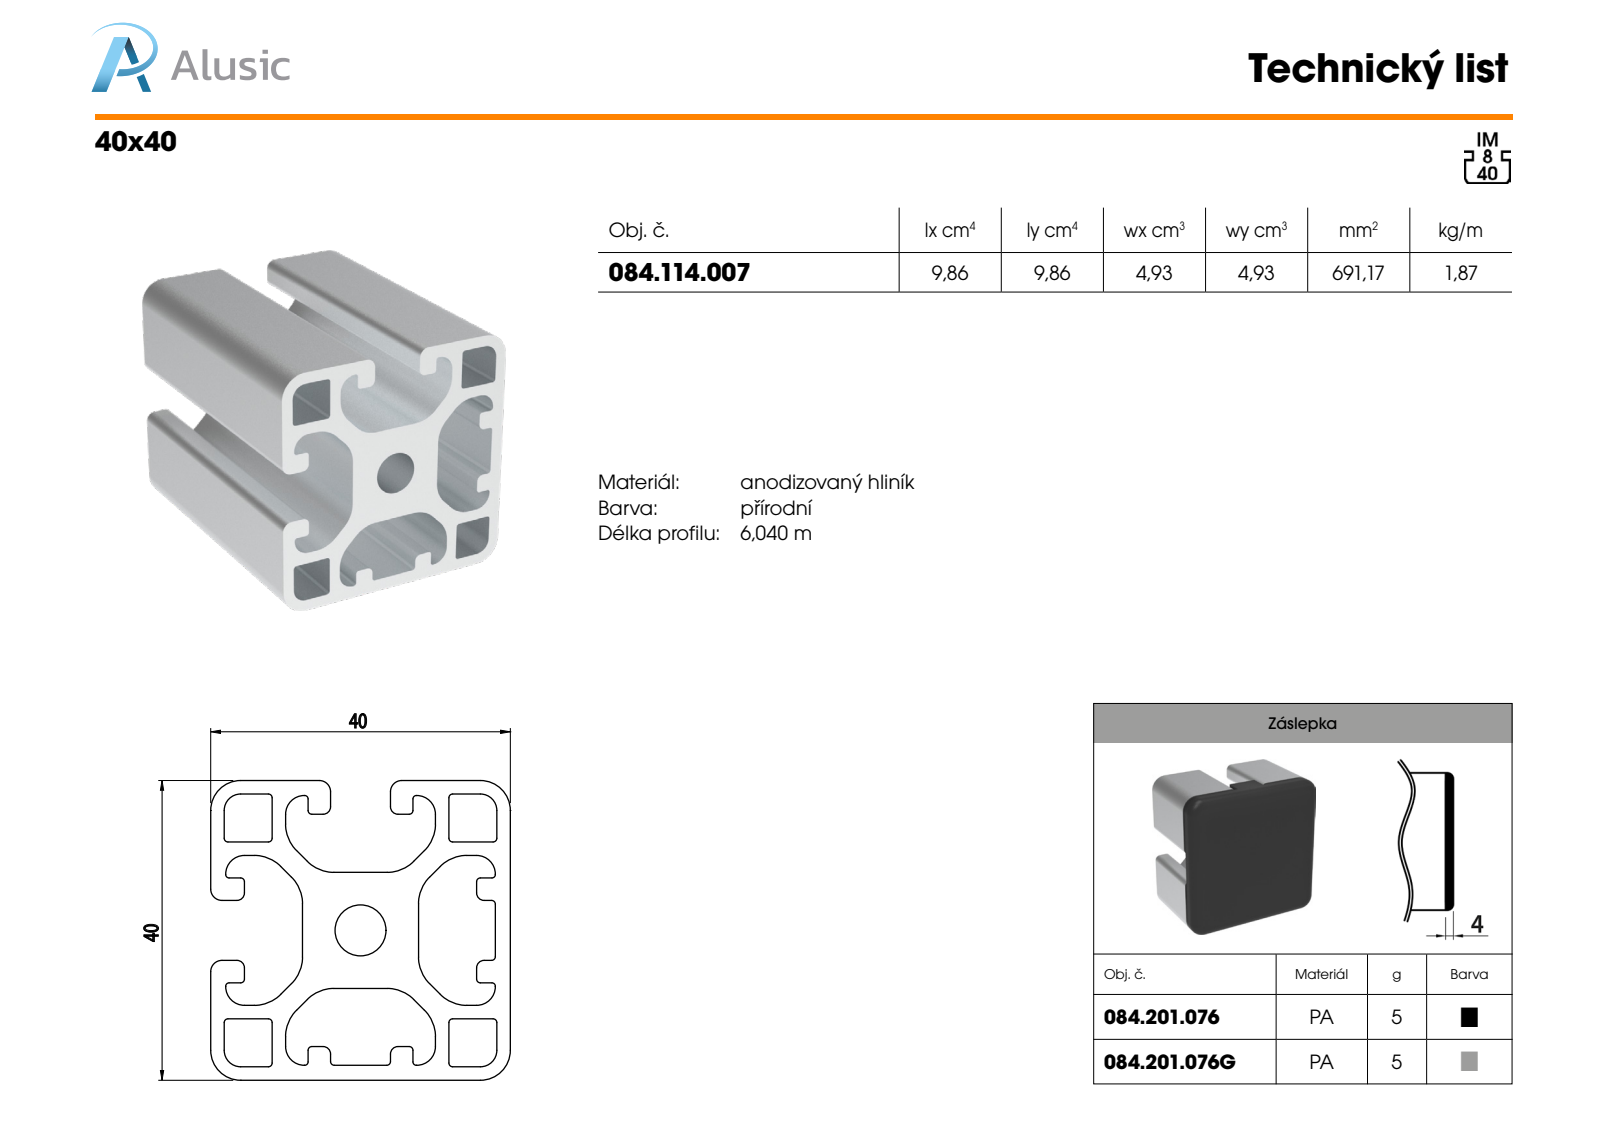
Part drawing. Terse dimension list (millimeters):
name: 084.114.007
written by: SolidWorks 2018 (AUTOMOTIVE_DESIGN)
unit: mm
bodies: 1 solid, 155 faces (77 planar, 78 cylindrical, 0 other)
size: 100 × 40 × 40
volume: 69 117 mm³; area: 49 972 mm²
holes: 1× ⌀6.8
rounds: 24× R0.5, 16× R5, 8× R0.45, 8× R1, 8× R2.5, 4× R1.5, 4× R2.2, 4× R4
face distances: 8.2, 31.8, 40, 30, 1.8, 3, 38.2, 6.4, 12.25, 27.75
